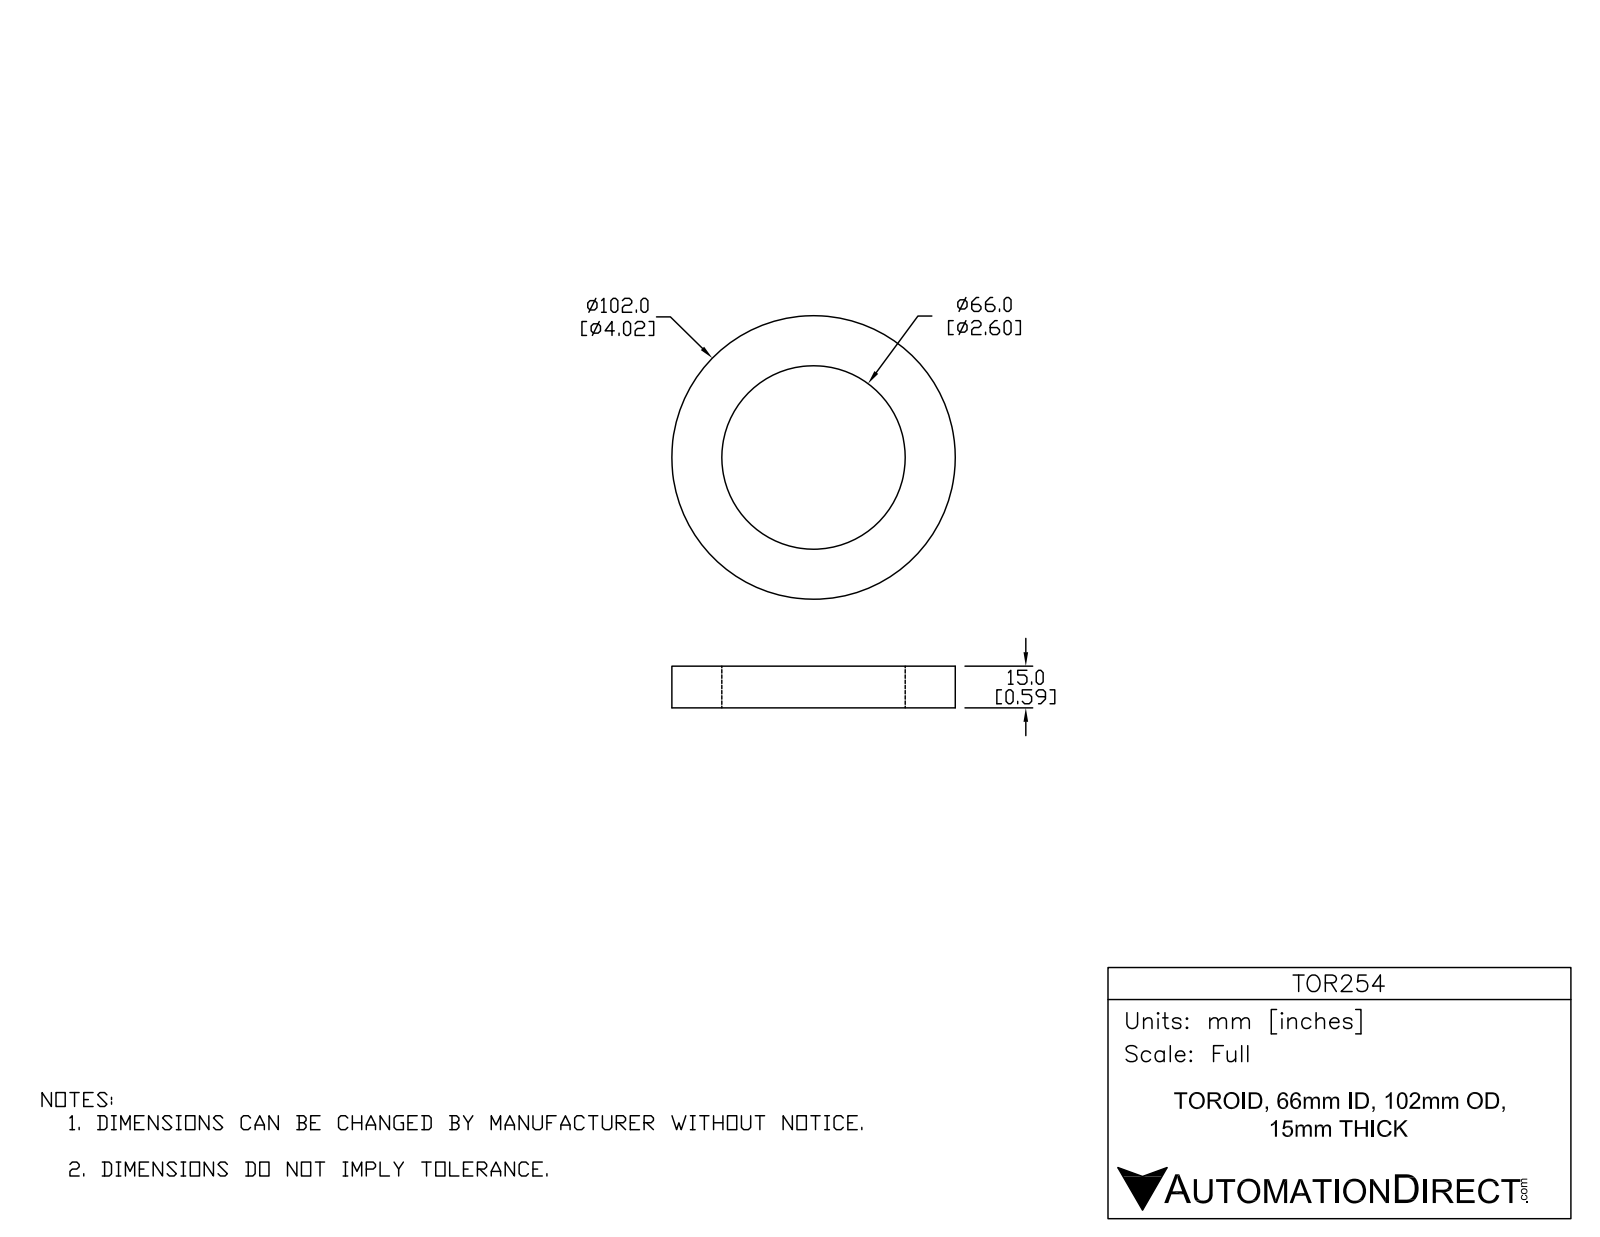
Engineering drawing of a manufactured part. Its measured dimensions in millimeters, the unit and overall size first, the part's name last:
Units: millimetres
Overall size (bounding box): 102 × 102 × 15
Round holes (diameter × count): ⌀66 ×1
Round bosses / shafts (diameter × count): ⌀102 ×1
Main face-to-face distances: 15
Volume: 71 251 mm³ · Surface area: 17 417 mm²
Bodies: 1 solid, 6 faces (2 planar, 4 cylindrical, 0 other)
Part name (STEP PRODUCT): TOR254
STEP written by: SolidWorks 2015 (AUTOMOTIVE_DESIGN)
